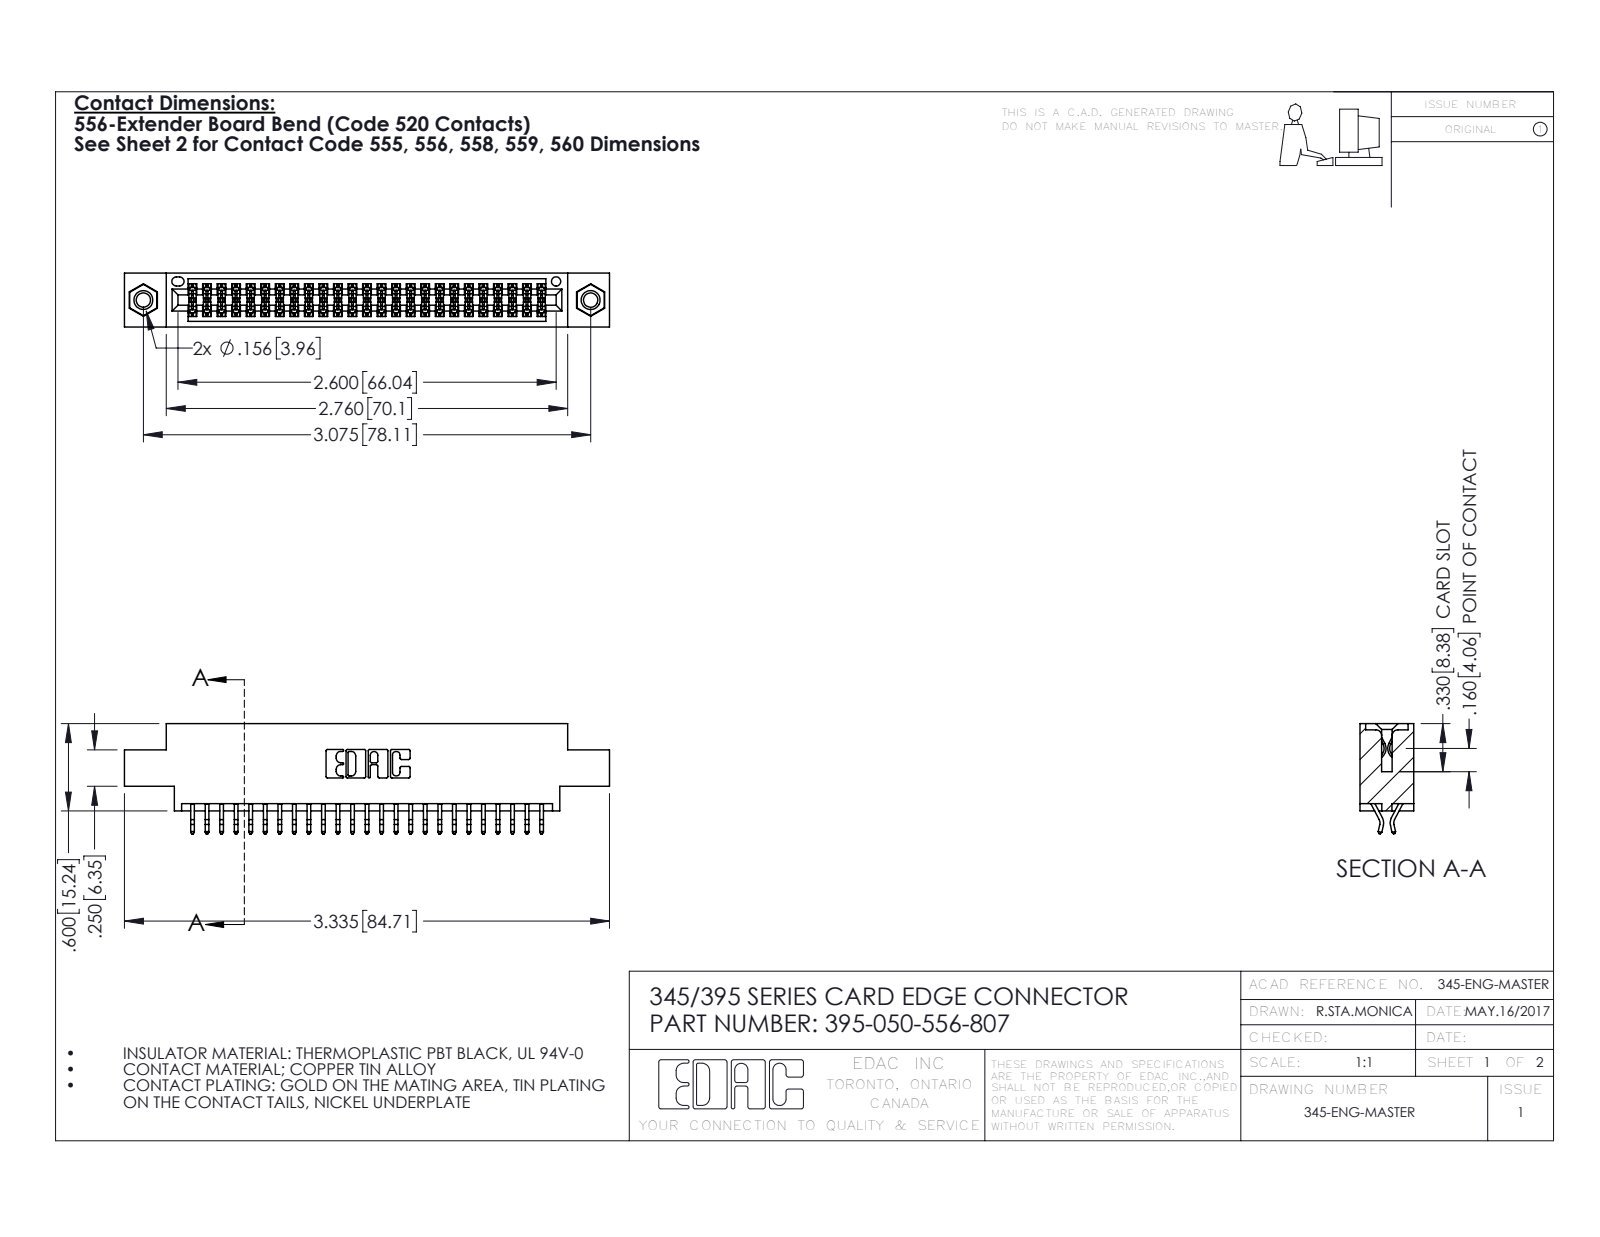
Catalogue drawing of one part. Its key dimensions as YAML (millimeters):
part_name: "395-050-556-807; 345-250-001_345-250-005-103; 345 Part_0.170 Offset - 0.156 Dia-TI; 345-292-001_556 Tail"
step_written_by: "SolidWorks 2016 (CONFIG_CONTROL_DESIGN)"
units: millimeters
bodies: {solids: 53, faces: 2990, planar: 1966, cylindrical: 1008, other: 16}
overall_size: [84.7, 19.2, 9.4]
volume: 7950
surface_area: 11540
round_holes:
  - {diameter: 2.5, count: 2}
  - {diameter: 3.2, count: 2}
  - {diameter: 4, count: 2}
  - {diameter: 1.6, count: 1}
round_bosses_or_shafts:
  - {diameter: 3.9, count: 2}
partial_cylinders:
  - {radius: 0.2, count: 75}
  - {radius: 0.3, count: 22}
  - {radius: 0.2, count: 6}
  - {radius: 0.8, count: 6}
  - {radius: 0.7, count: 3}
  - {radius: 0.3, count: 2}
  - {radius: 0.4, count: 2}
  - {radius: 0.5, count: 2}
face_to_face_distances: [1.8, 7.6, 9.4, 5.1, 0.6, 2.5, 6.9, 5.7, 4.4, 3.8]
hole_center_spacings: [6.9, 72.1, 78.1]
